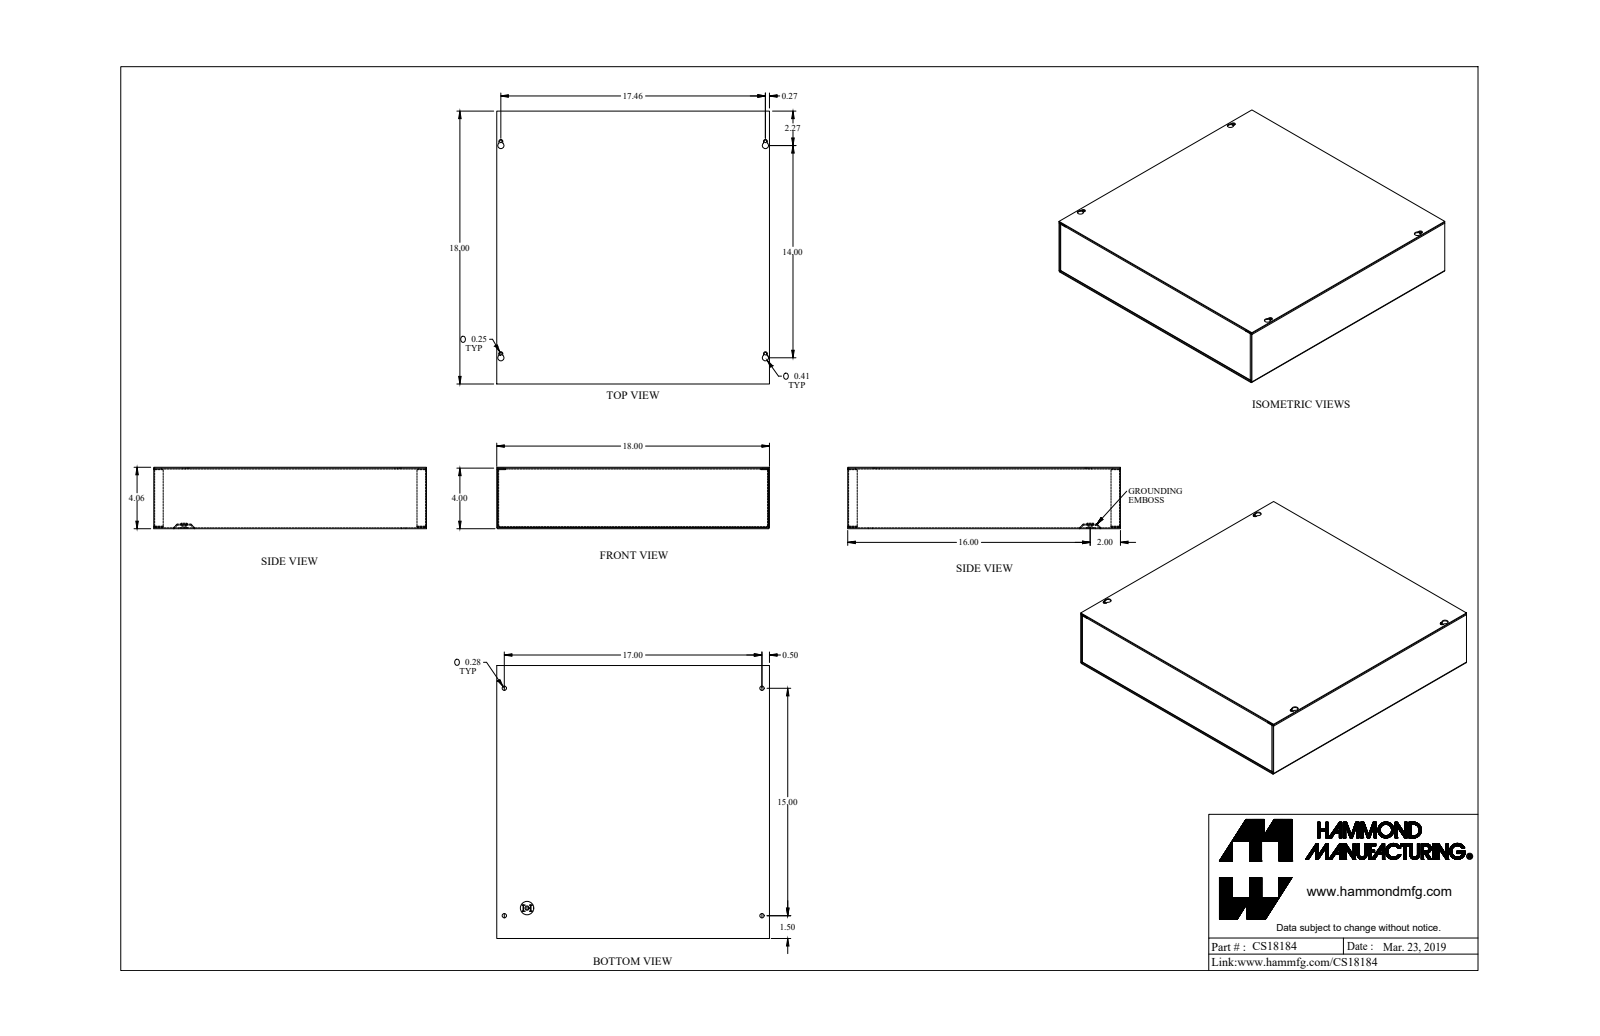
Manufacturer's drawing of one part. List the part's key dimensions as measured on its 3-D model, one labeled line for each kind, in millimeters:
Part name (STEP PRODUCT): CS18184_Default
STEP written by: SolidWorks 2019 (CONFIG_CONTROL_DESIGN)
Units: millimetres
Bodies: 4 solids, 205 faces (125 planar, 72 cylindrical, 8 other)
Overall size (bounding box): 457.2 × 457.2 × 103
Volume: 919 800 mm³ · Surface area: 1 281 000 mm²
Round holes (diameter × count): ⌀4.3 ×5, ⌀7.1 ×4, ⌀12.7 ×1
Round bosses / shafts (diameter × count): ⌀12.5 ×1, ⌀7.2 ×1
Partial cylindrical surfaces — rounded edges, fillets, slot ends (radius × count): R0.7 ×12, R2.2 ×12, R1.4 ×8, R3.2 ×4, R5.2 ×4
Main face-to-face distances: 1.4, 101.6, 100.2, 103, 455.8, 457.2, 454.3, 2, 98.1, 99.6
Hole centre spacings: 14, 368.4, 437.8, 572, 355.6, 381, 431.8, 443.5
